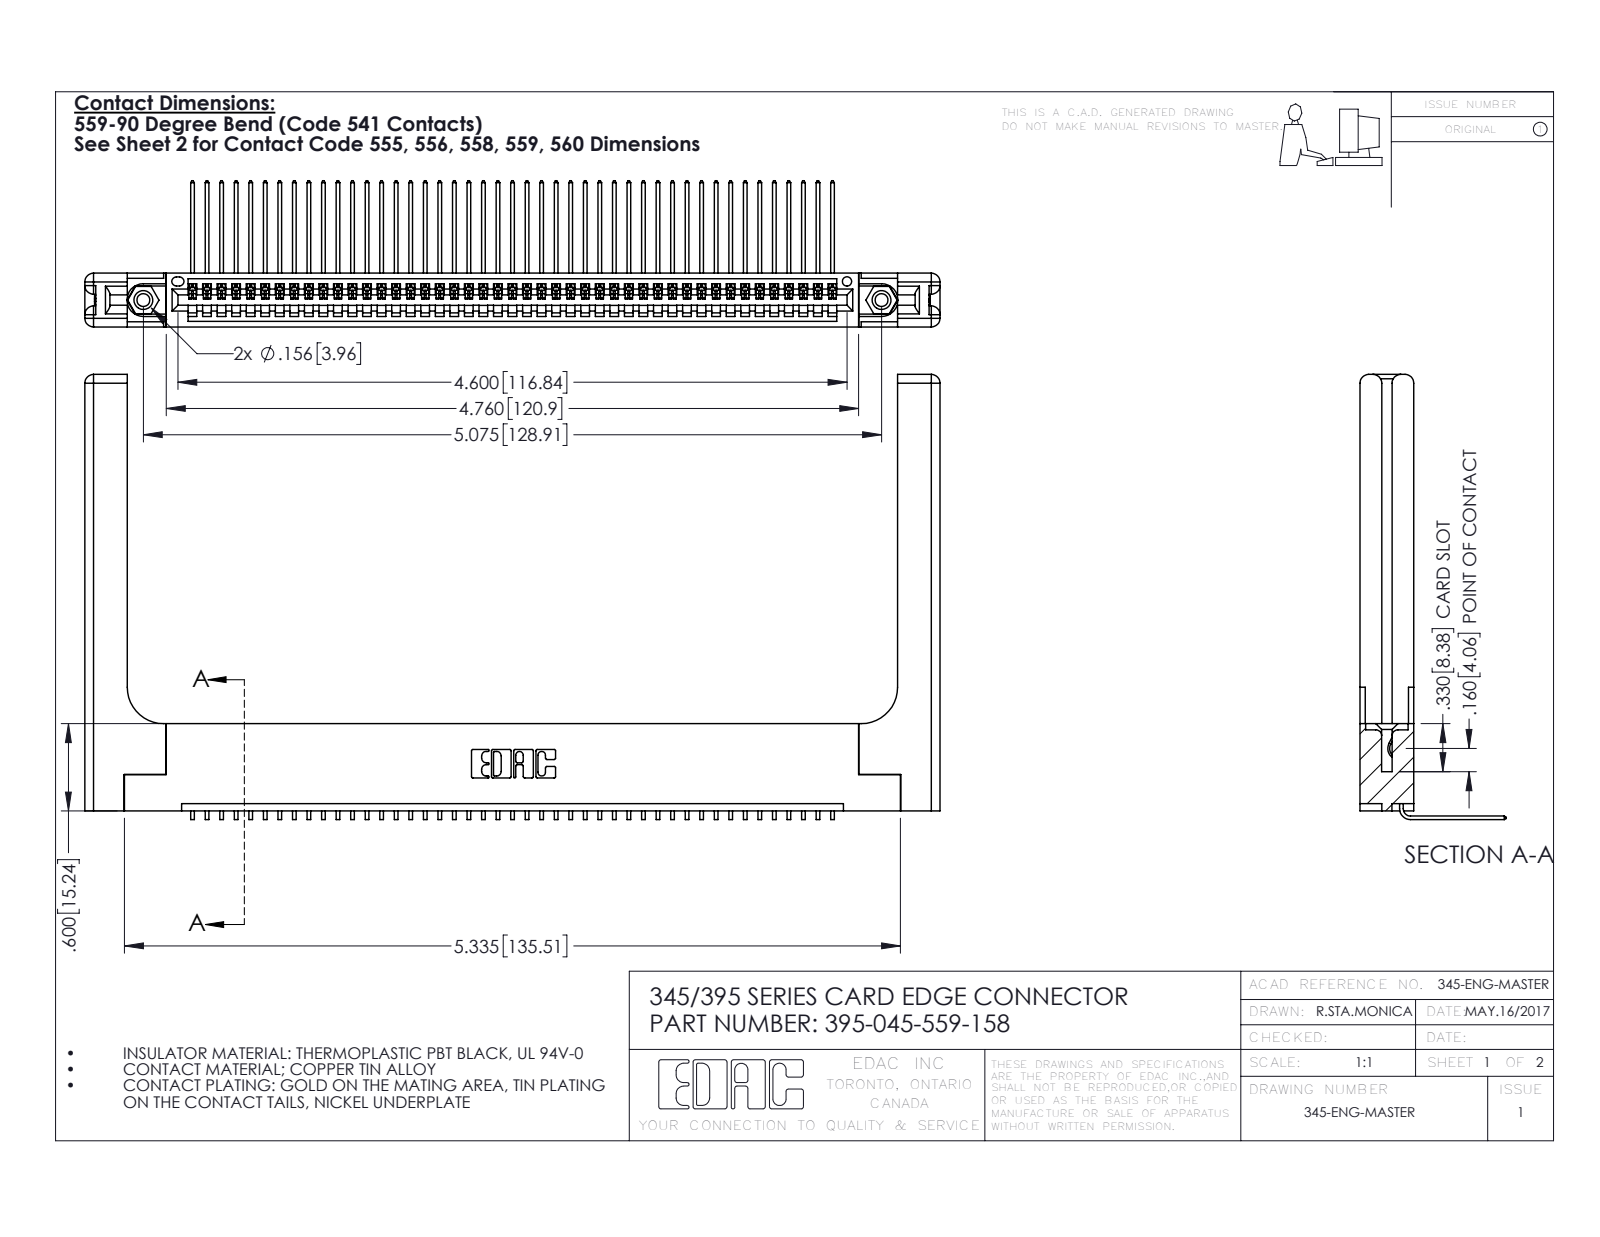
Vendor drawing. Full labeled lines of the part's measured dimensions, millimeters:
Part name (STEP PRODUCT): 345-220-058_345-220-058; 345-292-001_558 559 Tail - 1; 395-045-559-158; 345-250-001_345-250-001-102 (+1 more)
STEP written by: SolidWorks 2016 (CONFIG_CONTROL_DESIGN)
Units: millimetres
Bodies: 50 solids, 3082 faces (2118 planar, 904 cylindrical, 60 other)
Overall size (bounding box): 149.3 × 77.7 × 25.5
Volume: 22 860 mm³ · Surface area: 25 310 mm²
Round holes (diameter × count): ⌀2.3 ×2, ⌀3.2 ×2, ⌀4 ×2, ⌀1.6 ×1
Round bosses / shafts (diameter × count): ⌀3.9 ×2
Partial cylindrical surfaces — rounded edges, fillets, slot ends (radius × count): R0.2 ×90, R0.3 ×22, R1.5 ×16, R0.2 ×6, R0.8 ×6, R0.7 ×3, R0.8 ×2, R0.8 ×2
Main face-to-face distances: 9.4, 1.8, 7.6, 5.1, 2.5, 6.9, 0.6, 5.7, 3.8, 3.8
Hole centre spacings: 6.9, 122.9, 128.9
